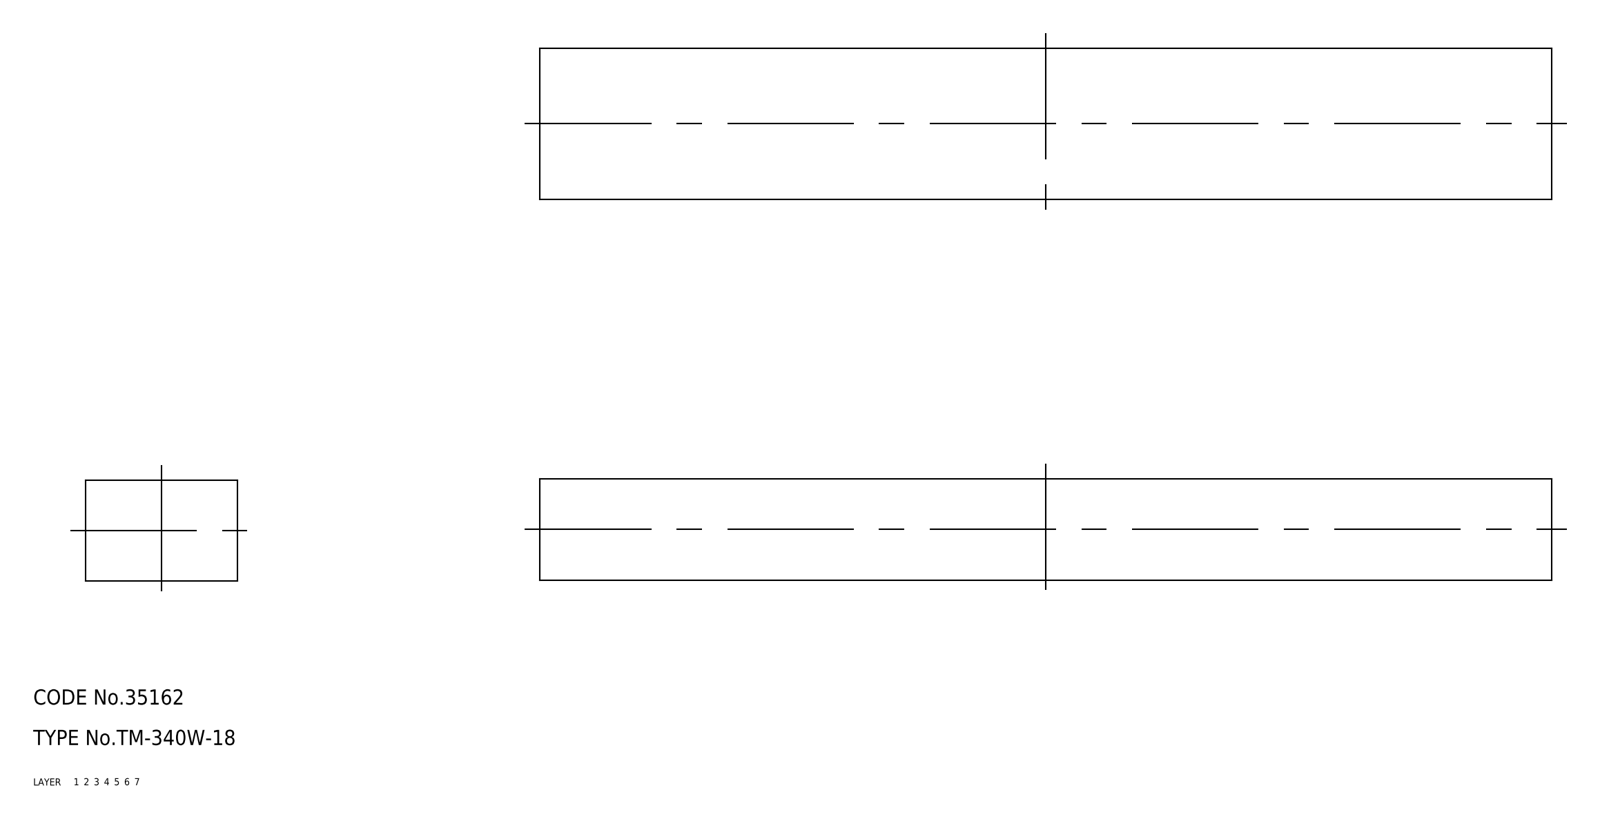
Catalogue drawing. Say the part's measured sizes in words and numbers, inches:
The part is named "TM_340W_18; rubber foam". Its 3-D file was written by "SolidWorks 2015 (AUTOMOTIVE_DESIGN)". It is 1 solid with 6 faces: 6 planar, 0 cylindrical and 0 other. Overall it measures 7.874 by 1.181 by 0.787 inches. Its volume is 7.323 cubic inches and its surface area 32.86 square inches. The main face-to-face distances are 0.787, 1.181, 7.874.
